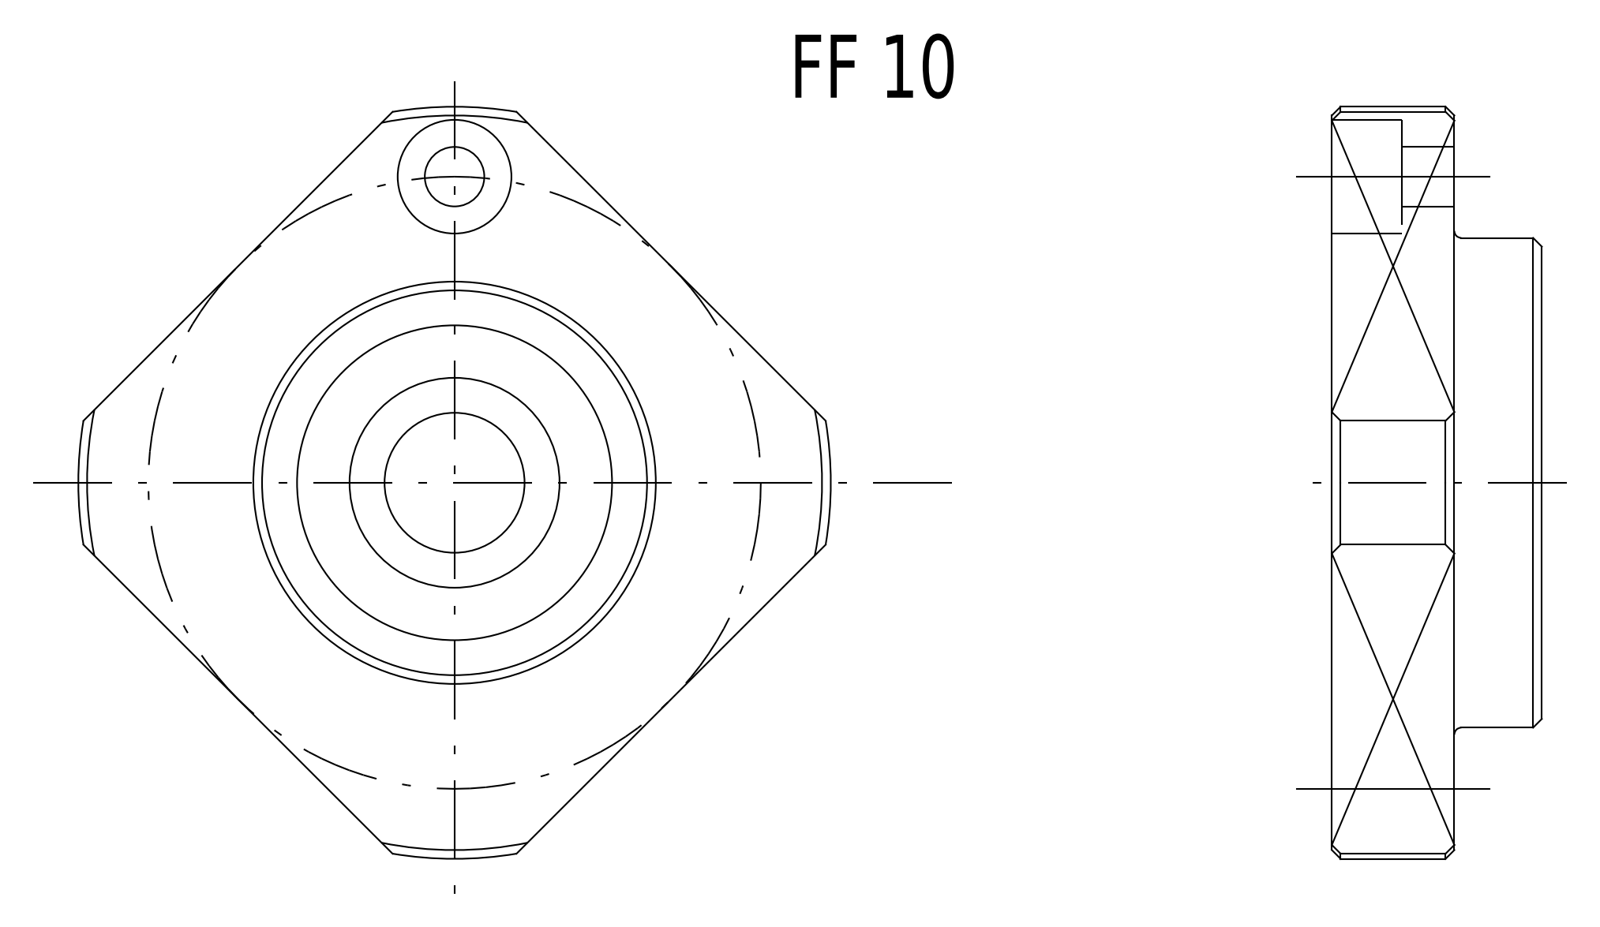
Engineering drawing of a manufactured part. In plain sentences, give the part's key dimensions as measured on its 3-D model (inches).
The part is named "FF10組合件". Its 3-D file was written by "SolidWorks 2008 (CONFIG_CONTROL_DESIGN)". It is 12 solids with 176 faces: 31 planar, 52 cylindrical and 93 other. Overall it measures 1.378 by 1.378 by 0.472 inches. Its volume is 0.467 cubic inches and its surface area 10.89 square inches. Round holes: 4 of diameter 0.134, 4 of diameter 0.256, 1 of diameter 0.315, 1 of diameter 0.432, 1 of diameter 0.715, 1 of diameter 0.768, 1 of diameter 0.866. Round bosses or shafts: 1 of diameter 1.102, 1 of diameter 0.478, 1 of diameter 0.415. Partial cylindrical surfaces (rounded edges, fillets, slot ends): 1 of radius 0.846. The main face-to-face distances are 0.276, 0.102, 0.37, 1.378, 0.02, 0.098, 0.122, 0.35, 0.248, 0.197. The hole center spacings are 0.689, 0.974, 1.378.
